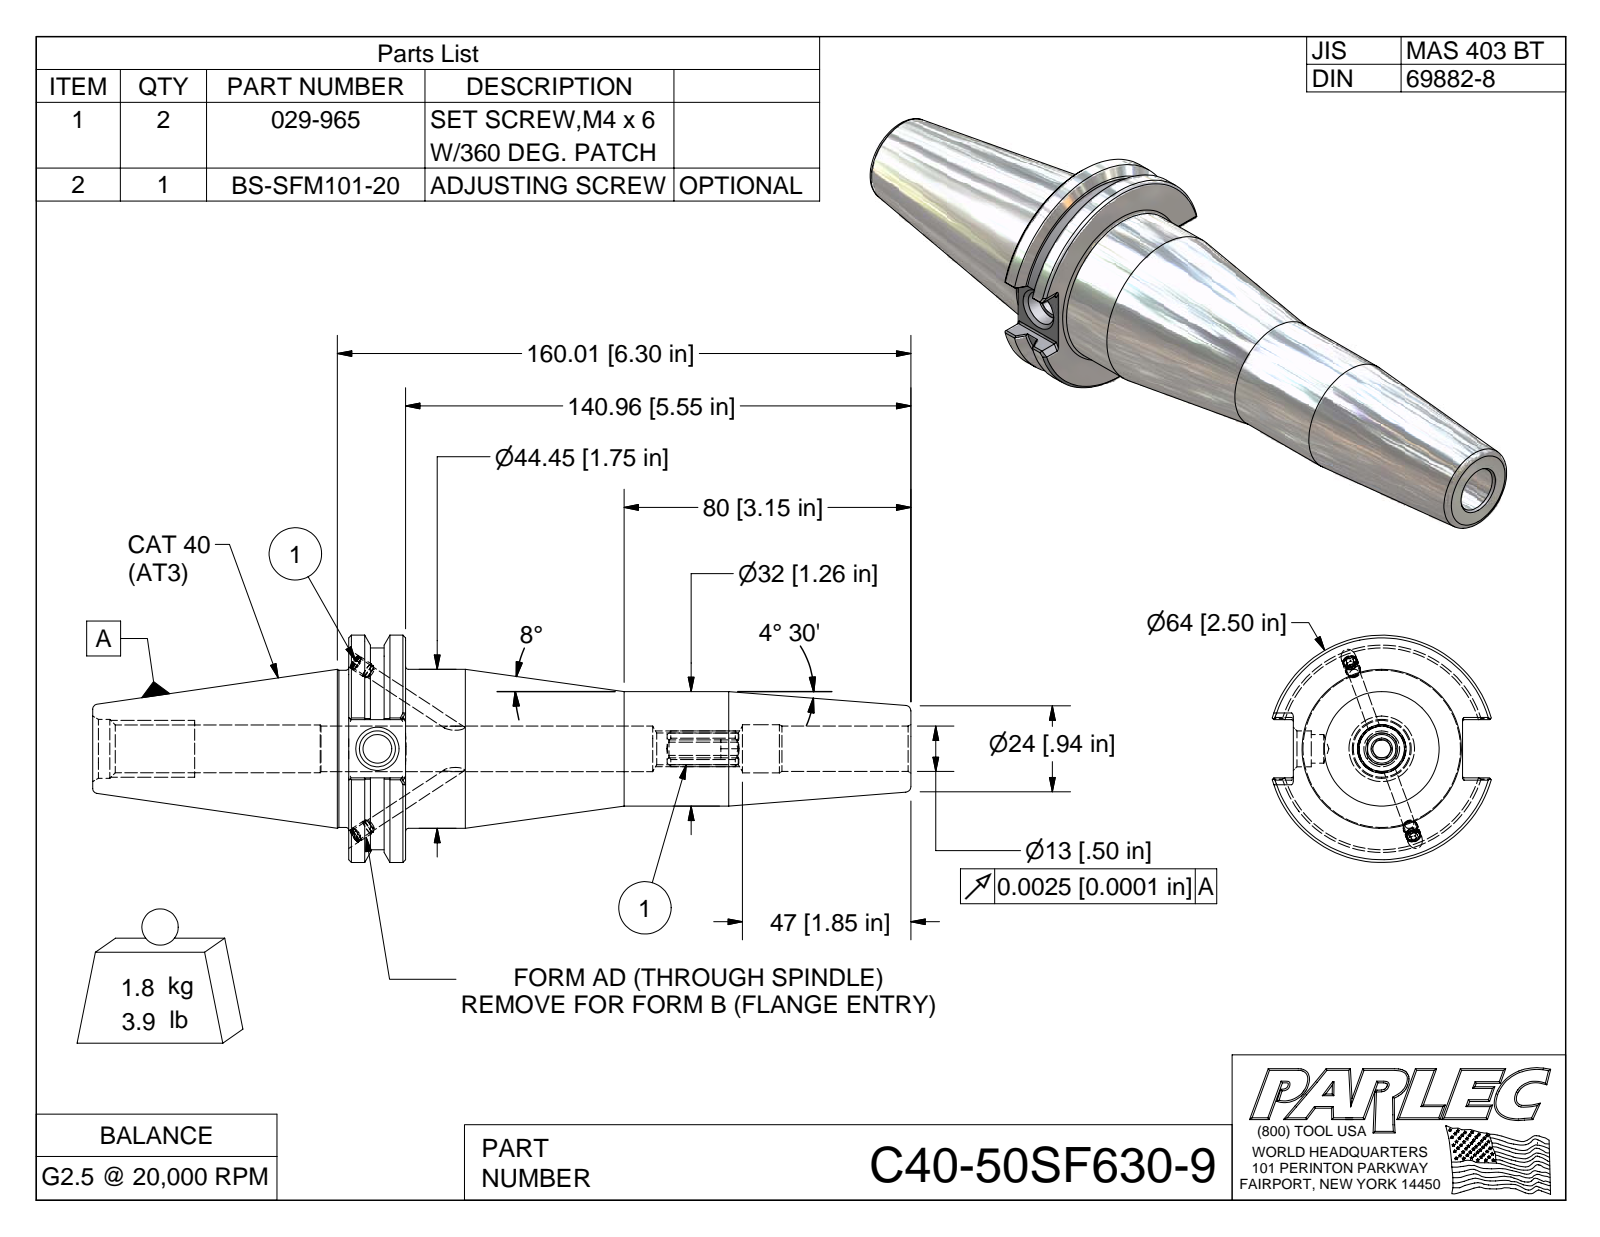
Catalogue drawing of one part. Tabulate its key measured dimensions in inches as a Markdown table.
| quantity | value |
| --- | --- |
| part name | C40-50SF630-9; C40BC-50SF630-9-1; 029-965; BS-SFM101-20 |
| STEP written by | Autodesk Inventor 2009 (AUTOMOTIVE_DESIGN) |
| units | inches |
| bodies | 4 solids, 154 faces (65 planar, 35 cylindrical, 54 other) |
| overall size | 8.987 × 2.5 × 2.406 |
| volume | 13.23 in³ |
| surface area | 64.23 in² |
| round holes (diameter × count) | 0.13 × 2, 0.161 × 2, 0.499 × 1, 0.529 × 1 |
| round bosses / shafts (diameter × count) | 0.165 × 2, 0.157 × 2, 2.5 × 1, 2.219 × 1, 1.75 × 1, 1.73 × 1, 1.26 × 1 |
| partial cylindrical surfaces (radius × count) | 0.02 × 12, 0.197 × 1 |
| main face-to-face distances | 0.625, 6.175, 5.55, 0.64, 1.86, 2.812, 3.437, 8.987, 0.236, 1.046 |
